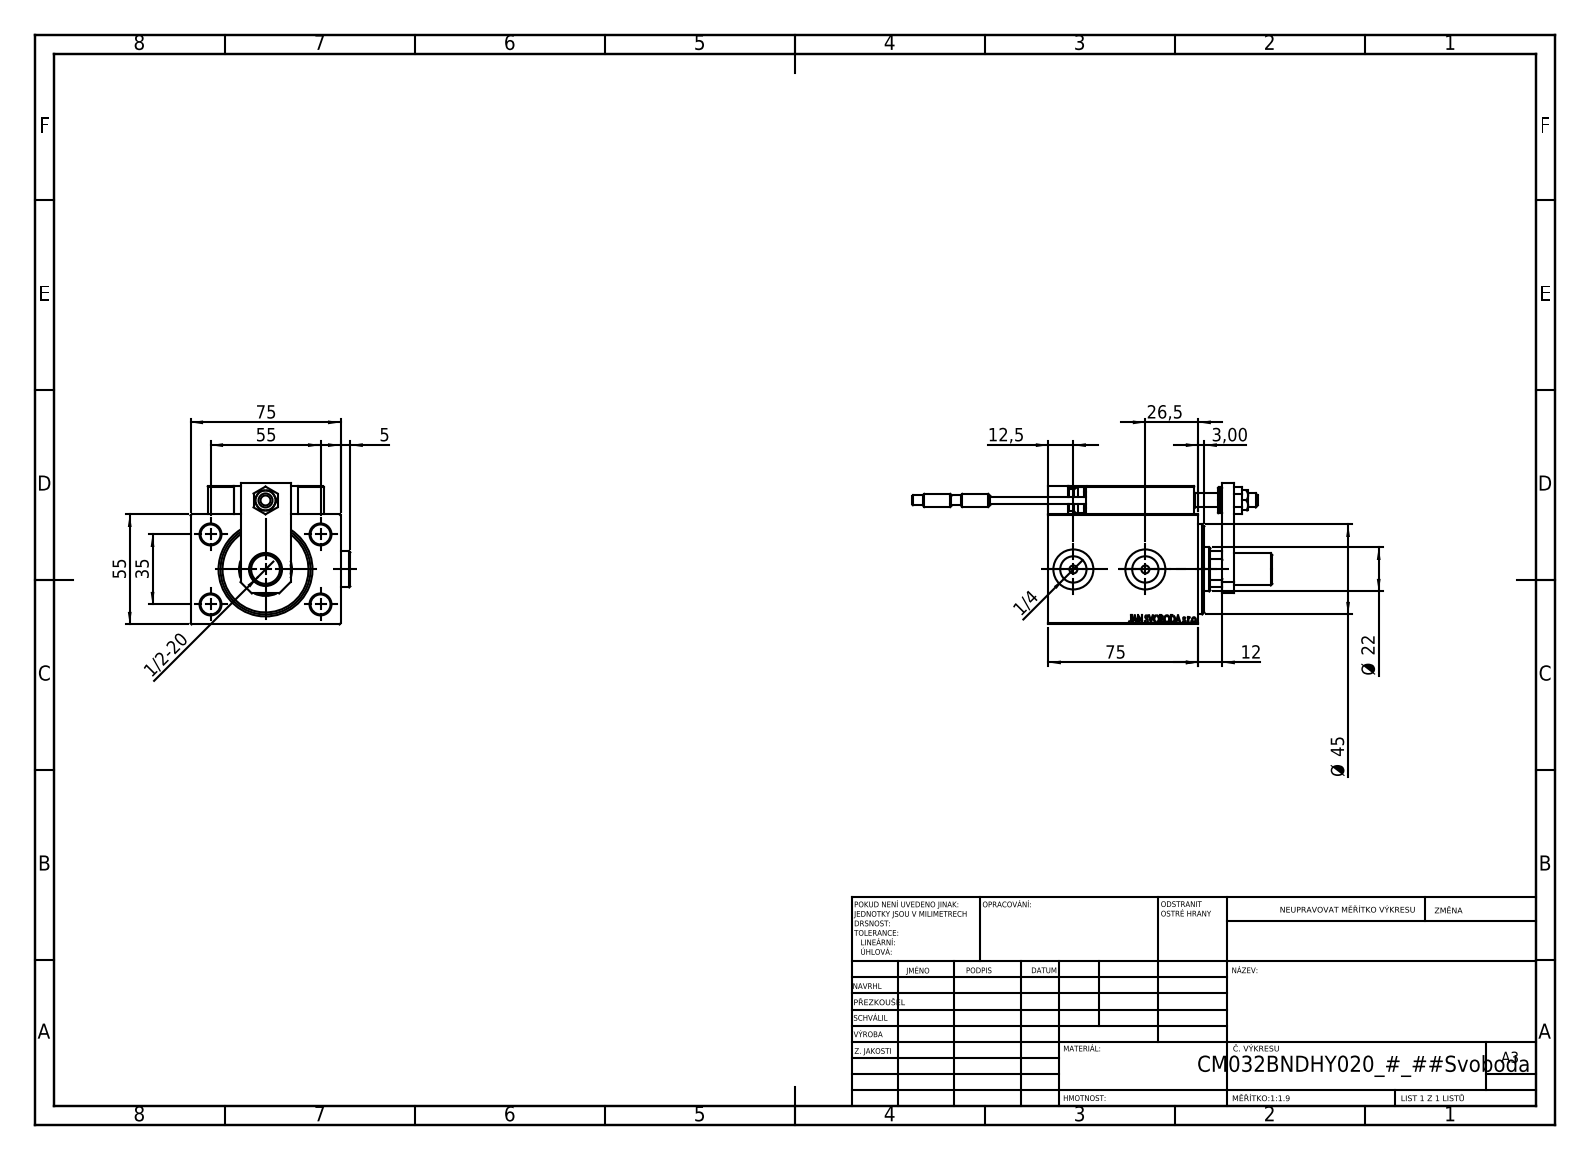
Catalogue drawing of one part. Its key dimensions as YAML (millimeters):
part_name: "SWITCH_X_FRONT_BACK; Block; V450CM_B_Body; MAGNET (+8 more)"
step_written_by: "SolidWorks 2019 (CONFIG_CONTROL_DESIGN)"
units: millimeters
bodies: {solids: 27, faces: 1407, planar: 600, cylindrical: 212, other: 595}
overall_size: [180, 79.9, 70.5]
volume: 341829
surface_area: 84335
round_holes:
  - {diameter: 4, count: 6}
  - {diameter: 8, count: 5}
  - {diameter: 3.2, count: 4}
  - {diameter: 10, count: 4}
  - {diameter: 5, count: 2}
  - {diameter: 13.16, count: 2}
  - {diameter: 20, count: 2}
  - {diameter: 7, count: 1}
  - {diameter: 10.5, count: 1}
  - {diameter: 16.5, count: 1}
  - {diameter: 22, count: 1}
  - {diameter: 25.5, count: 1}
round_bosses_or_shafts:
  - {diameter: 5, count: 4}
  - {diameter: 18, count: 2}
  - {diameter: 6.5, count: 2}
  - {diameter: 3.8, count: 2}
  - {diameter: 16, count: 1}
  - {diameter: 14, count: 1}
  - {diameter: 13, count: 1}
  - {diameter: 11, count: 1}
partial_cylinders:
  - {radius: 0.3, count: 30}
  - {radius: 3, count: 2}
  - {radius: 10.5, count: 1}
face_to_face_distances: [55, 75, 12, 10, 14, 69, 25, 5, 7, 65]
hole_center_spacings: [32.6, 11.37, 20, 27.07, 29.59, 29.69, 32.33, 34.83]
